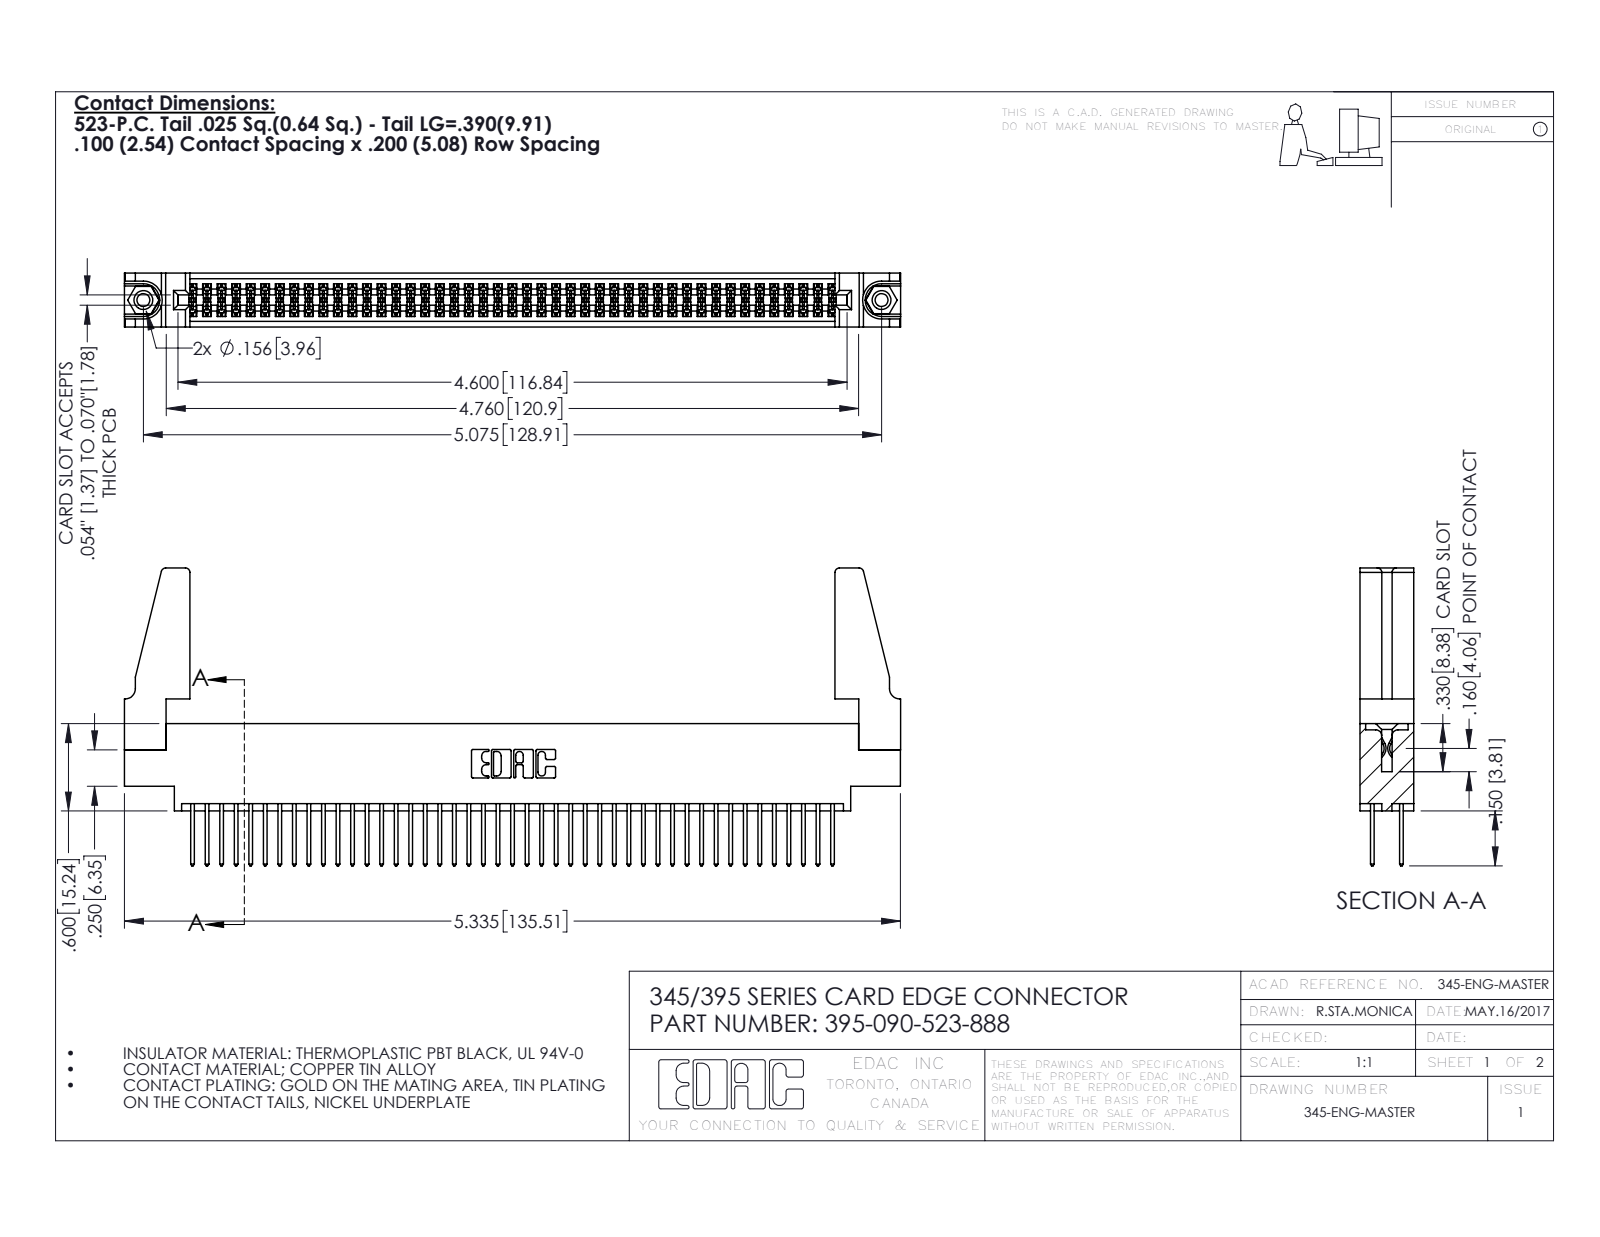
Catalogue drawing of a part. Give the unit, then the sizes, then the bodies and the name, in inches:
Units: inches
Overall size (bounding box): 5.336 × 2.047 × 0.37
Round holes (diameter × count): ⌀0.089 ×2, ⌀0.125 ×2, ⌀0.156 ×2, ⌀0.064 ×1
Round bosses / shafts (diameter × count): ⌀0.155 ×2
Partial cylindrical surfaces — rounded edges, fillets, slot ends (radius × count): R0.006 ×135, R0.01 ×90, R0.01 ×22, R0.03 ×8, R0.007 ×6, R0.031 ×6, R0.026 ×3, R0.014 ×2
Main face-to-face distances: 0.072, 0.298, 0.37, 0.2, 0.098, 0.272, 0.025, 0.225, 0.175, 0.149
Hole centre spacings: 0.27, 4.839, 5.075
Volume: 1.008 in³ · Surface area: 36.83 in²
Bodies: 95 solids, 4754 faces (3126 planar, 1612 cylindrical, 16 other)
Part name (STEP PRODUCT): 345 Part_0.170 Offset - 0.156 Dia-TH; 345-292-001_345-293-123; 345-250-001_345-250-001-102; 395-090-523-888 (+1 more)
STEP written by: SolidWorks 2016 (CONFIG_CONTROL_DESIGN)
